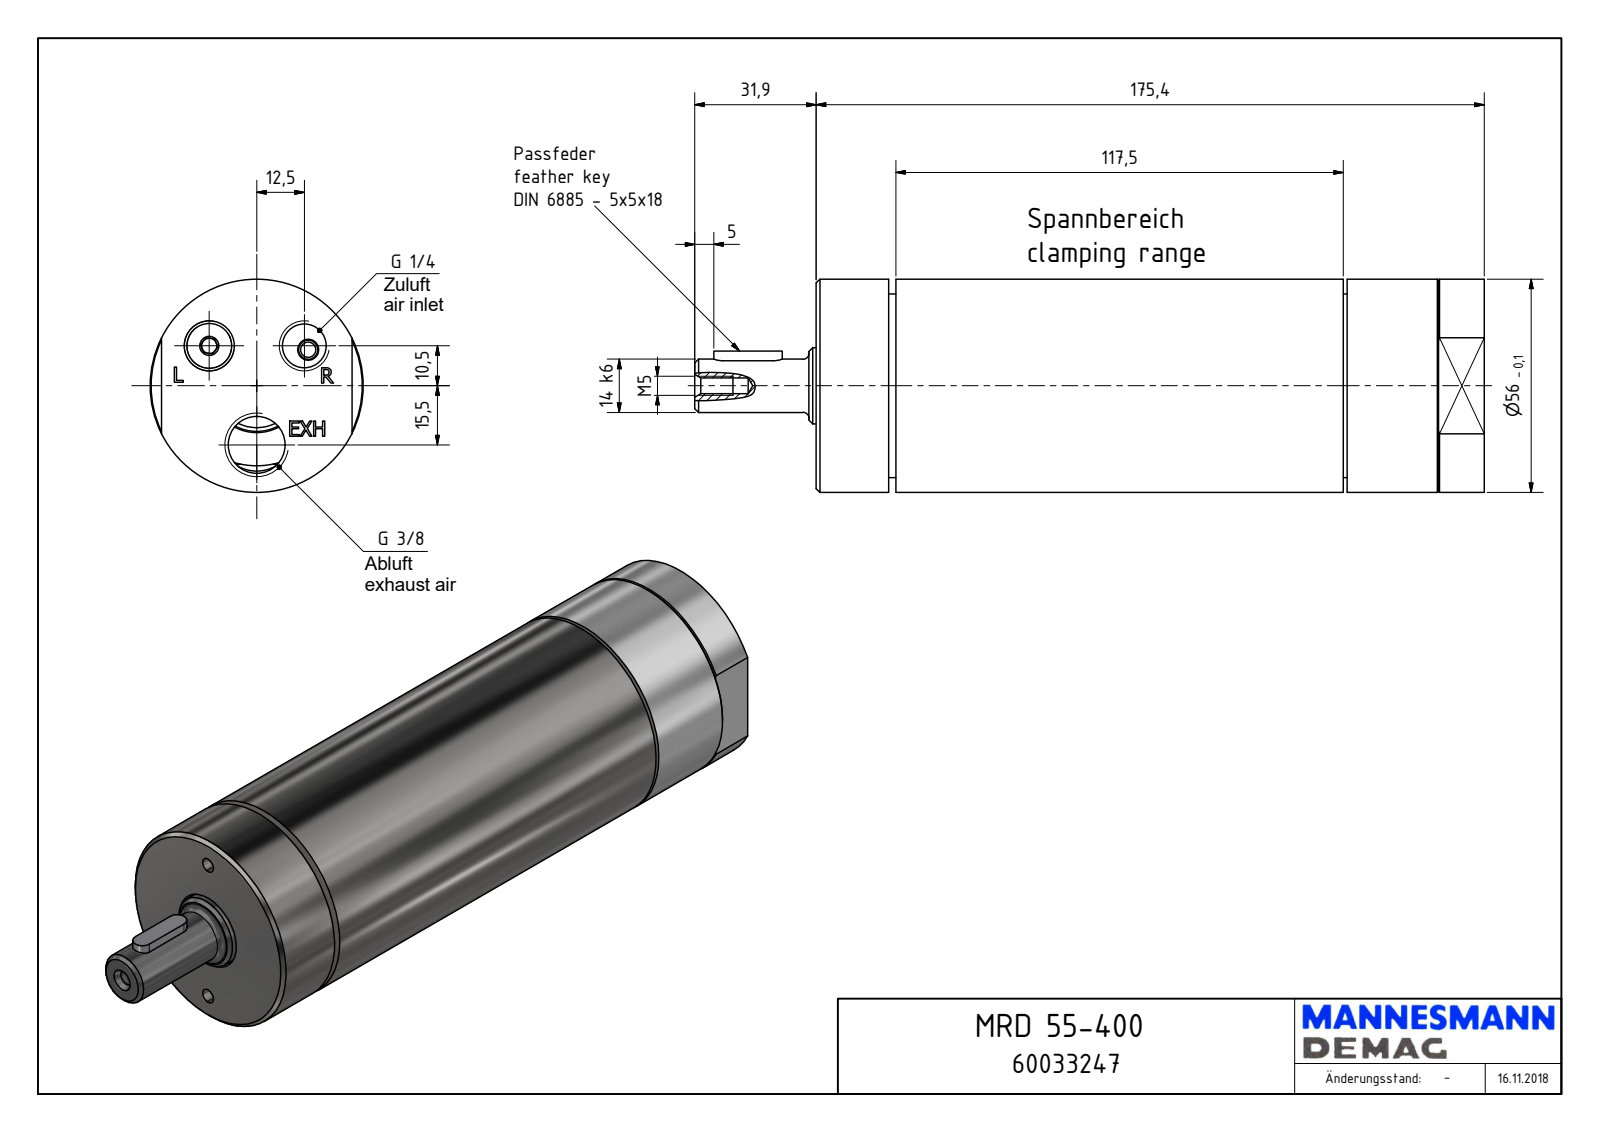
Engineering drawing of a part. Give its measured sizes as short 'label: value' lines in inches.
name: MRD 55-400_60033247
written by: Autodesk Inventor 2018 (AUTOMOTIVE_DESIGN)
unit: in
bodies: 1 solid, 168 faces (102 planar, 24 cylindrical, 42 other)
size: 8.161 × 2.205 × 2.205
volume: 26.32 in³; area: 66.05 in²
holes: 3× ⌀0.157, 1× ⌀0.163, 1× ⌀0.451, 1× ⌀0.589, 1× ⌀0.827, 1× ⌀0.837, 1× ⌀0.927, 1× ⌀1.024, 1× ⌀1.905
bosses: 1× ⌀2.205, 1× ⌀1.897, 1× ⌀0.785, 1× ⌀0.551
rounds: 2× R0.098
face distances: 6.906, 0.823, 6.083, 5.449, 4.626, 1.457, 0.075, 5.488, 0.748, 4.701
hole spacings: 0.643, 0.827, 1.136, 1.334, 0.217, 0.61, 0.984, 1.437
